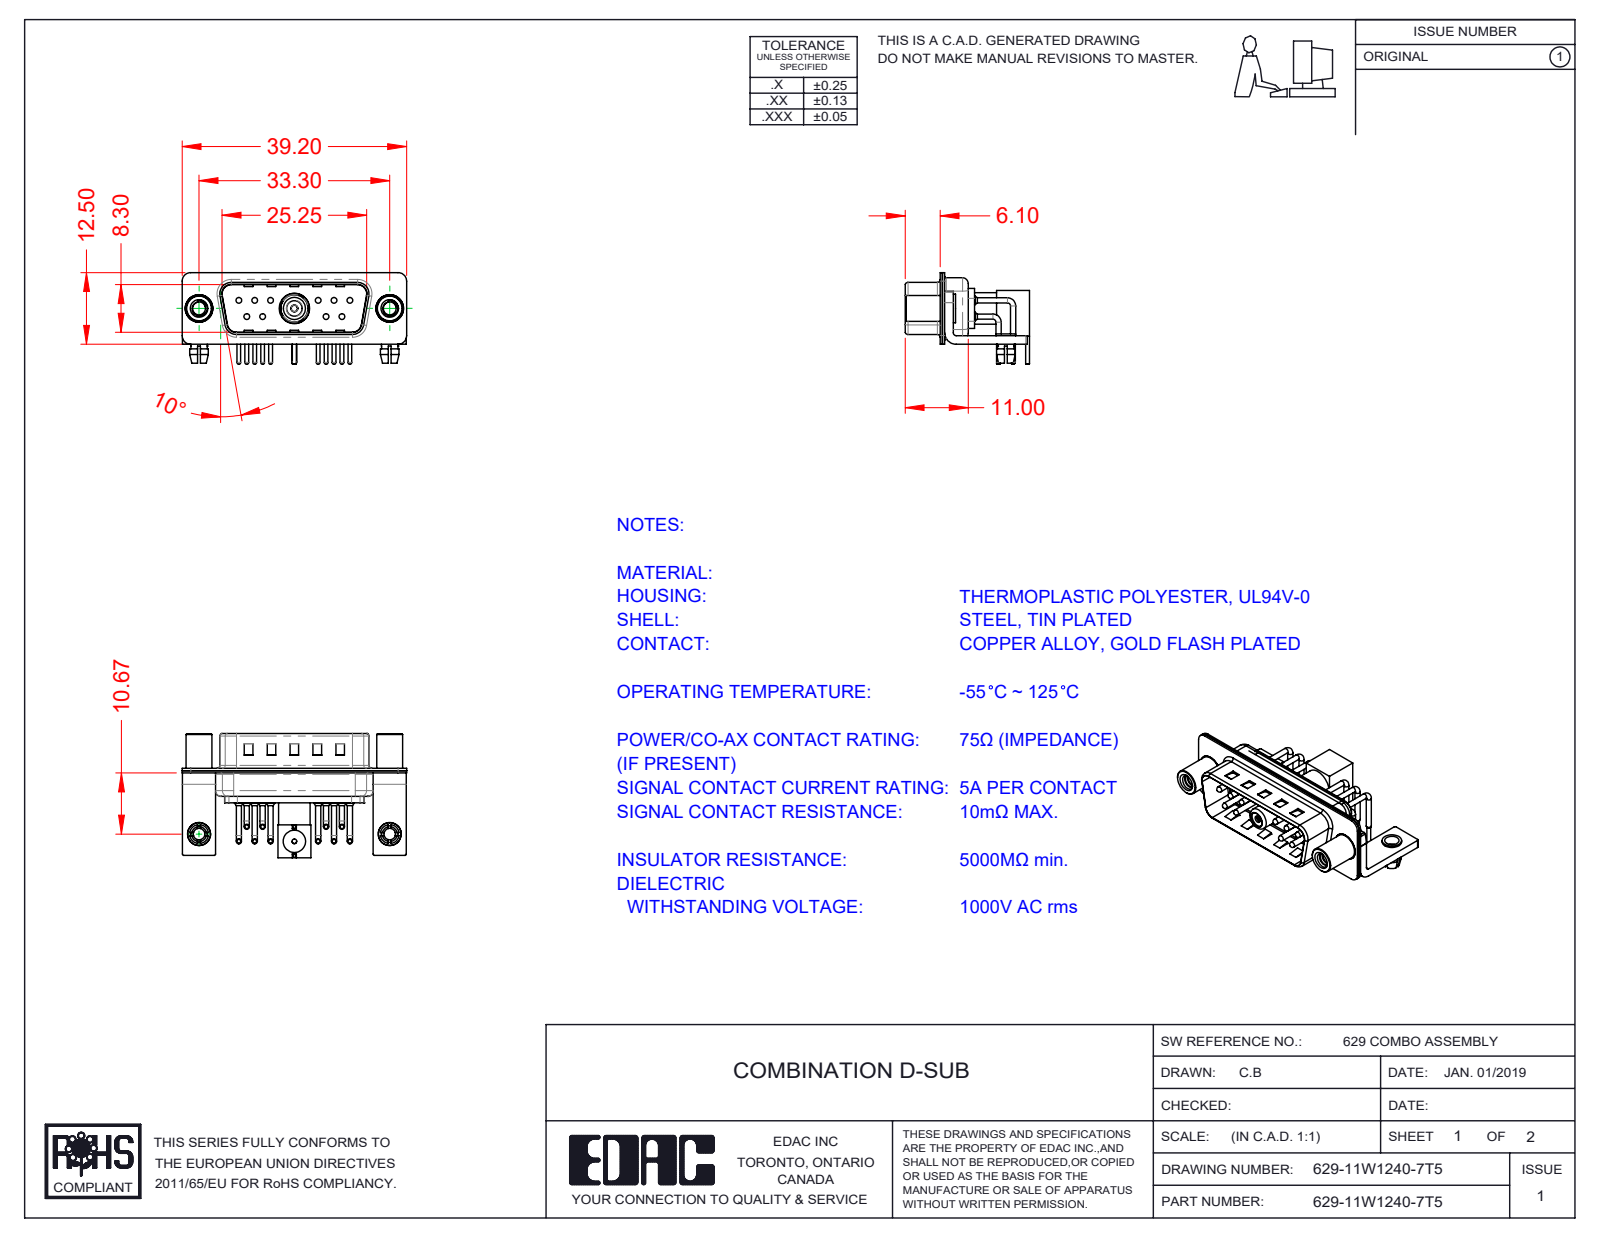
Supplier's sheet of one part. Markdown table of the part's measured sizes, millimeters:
| quantity | value |
| --- | --- |
| part name | RA Back Shell; 629-11W1240-7T5; 629Combo Threaded Standoff_5; 629Combo Board Lock (+8 more) |
| STEP written by | SolidWorks 2020 (CONFIG_CONTROL_DESIGN) |
| units | millimeters |
| bodies | 26 solids, 1785 faces (915 planar, 656 cylindrical, 214 other) |
| overall size | 39.2 × 21.71 × 16 |
| volume | 2 644 mm³ |
| surface area | 7 203 mm² |
| round holes (diameter × count) | 2 × 12, 1.6 × 11, 0.75 × 10, 2.5 × 3, 2.26 × 2, 3.2 × 2, 4 × 2, 4.8 × 2, 0.8 × 1, 1.1 × 1, 1.2 × 1, 1.5 × 1 |
| round bosses / shafts (diameter × count) | 0.9 × 20, 1.5 × 10, 1 × 10, 0.65 × 10, 4 × 3, 3.3 × 3, 2.9 × 3, 5 × 2 |
| partial cylindrical surfaces (radius × count) | 0.25 × 16, 1.5 × 16, 2 × 13, 1.01 × 10, 0.5 × 9, 1.6 × 8, 1 × 7, 0.6 × 4 |
| main face-to-face distances | 0.4, 0.8, 1.5, 9.5, 9.1, 8.7, 9.9, 0.6, 1.9, 0.35 |
| hole center spacings | 3.16, 2.77, 13.85, 16.7, 11.08, 16.62, 5.03, 5.04 |
